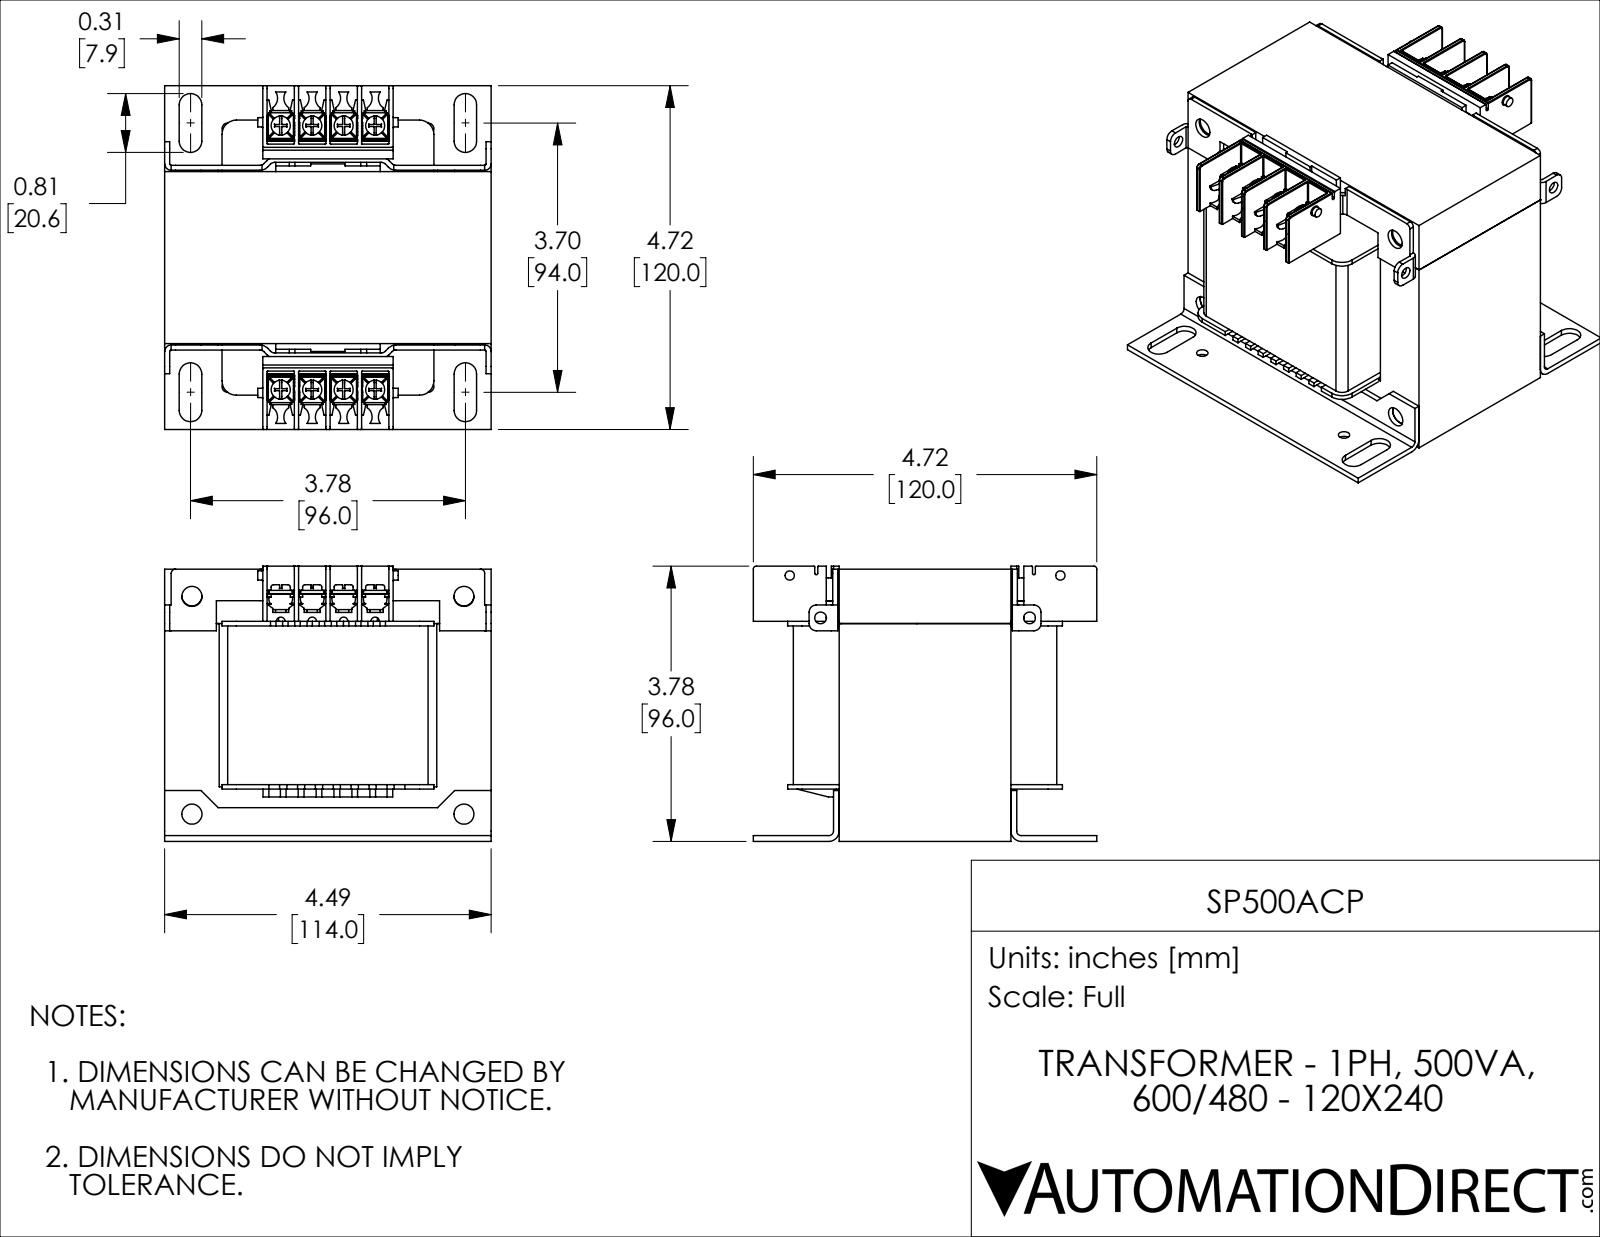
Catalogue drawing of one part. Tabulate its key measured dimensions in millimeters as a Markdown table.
| quantity | value |
| --- | --- |
| part name | SP500ACP |
| STEP written by | SolidWorks 2018 (AUTOMOTIVE_DESIGN) |
| units | millimeters |
| bodies | 42 solids, 3287 faces (2027 planar, 960 cylindrical, 300 other) |
| overall size | 120 × 114 × 96 |
| volume | 799 500 mm³ |
| surface area | 174 600 mm² |
| round holes (diameter × count) | 4 × 13, 2.7 × 8, 3.5 × 8, 7 × 6, 4.1 × 2, 4.5 × 2 |
| round bosses / shafts (diameter × count) | 6.7 × 8, 6.1 × 8, 4.3 × 8, 2.8 × 8, 3.3 × 2 |
| partial cylindrical surfaces (radius × count) | 0.1 × 52, 0.3 × 52, 0.3 × 42, 0.7 × 32, 0.9 × 20, 4 × 16, 0.9 × 12, 2 × 10 |
| main face-to-face distances | 76, 19, 16, 95, 92, 22, 0.5, 60, 38, 2 |
| hole center spacings | 11, 22, 92.6, 33, 40.5, 51.5, 91.9, 94.5 |
